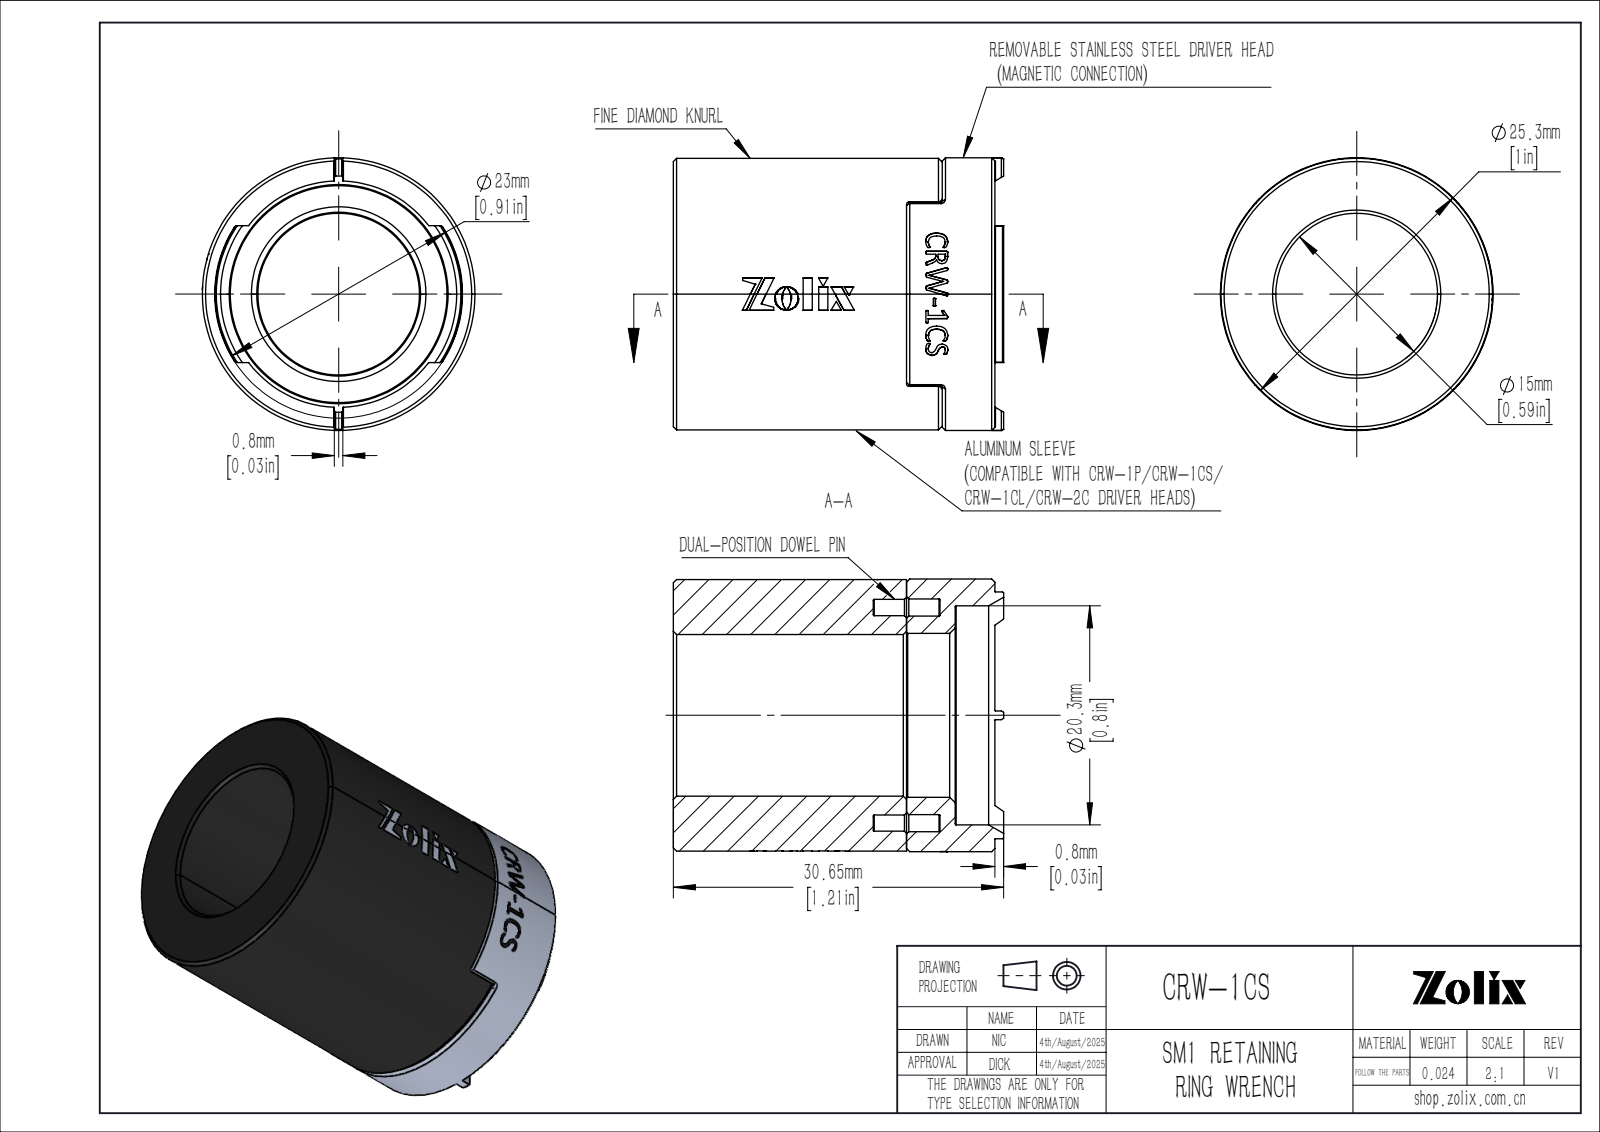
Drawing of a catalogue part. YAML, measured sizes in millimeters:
part_name: "CRW-1CS"
step_written_by: "SolidWorks 2020 (CONFIG_CONTROL_DESIGN)"
units: millimeters
bodies: {solids: 2, faces: 483, planar: 77, cylindrical: 72, other: 334}
overall_size: [30.65, 25.3, 25.3]
volume: 8801
surface_area: 5644
round_holes:
  - {diameter: 3, count: 4}
  - {diameter: 1.5, count: 2}
  - {diameter: 1.6, count: 2}
  - {diameter: 15, count: 1}
  - {diameter: 15.2, count: 1}
  - {diameter: 20.32, count: 1}
round_bosses_or_shafts:
  - {diameter: 25.3, count: 1}
  - {diameter: 25.2, count: 1}
partial_cylinders:
  - {radius: 0.1, count: 2}
  - {radius: 0.2, count: 2}
  - {radius: 11.45, count: 1}
  - {radius: 12.58, count: 1}
  - {radius: 12.63, count: 1}
face_to_face_distances: [21.65, 4.5, 26.15, 17.05, 29.85, 8.2, 3.7, 4.9, 24.95, 3.3]
hole_center_spacings: [5.18, 9.99, 10, 19.31, 17.3, 19.98, 20]
